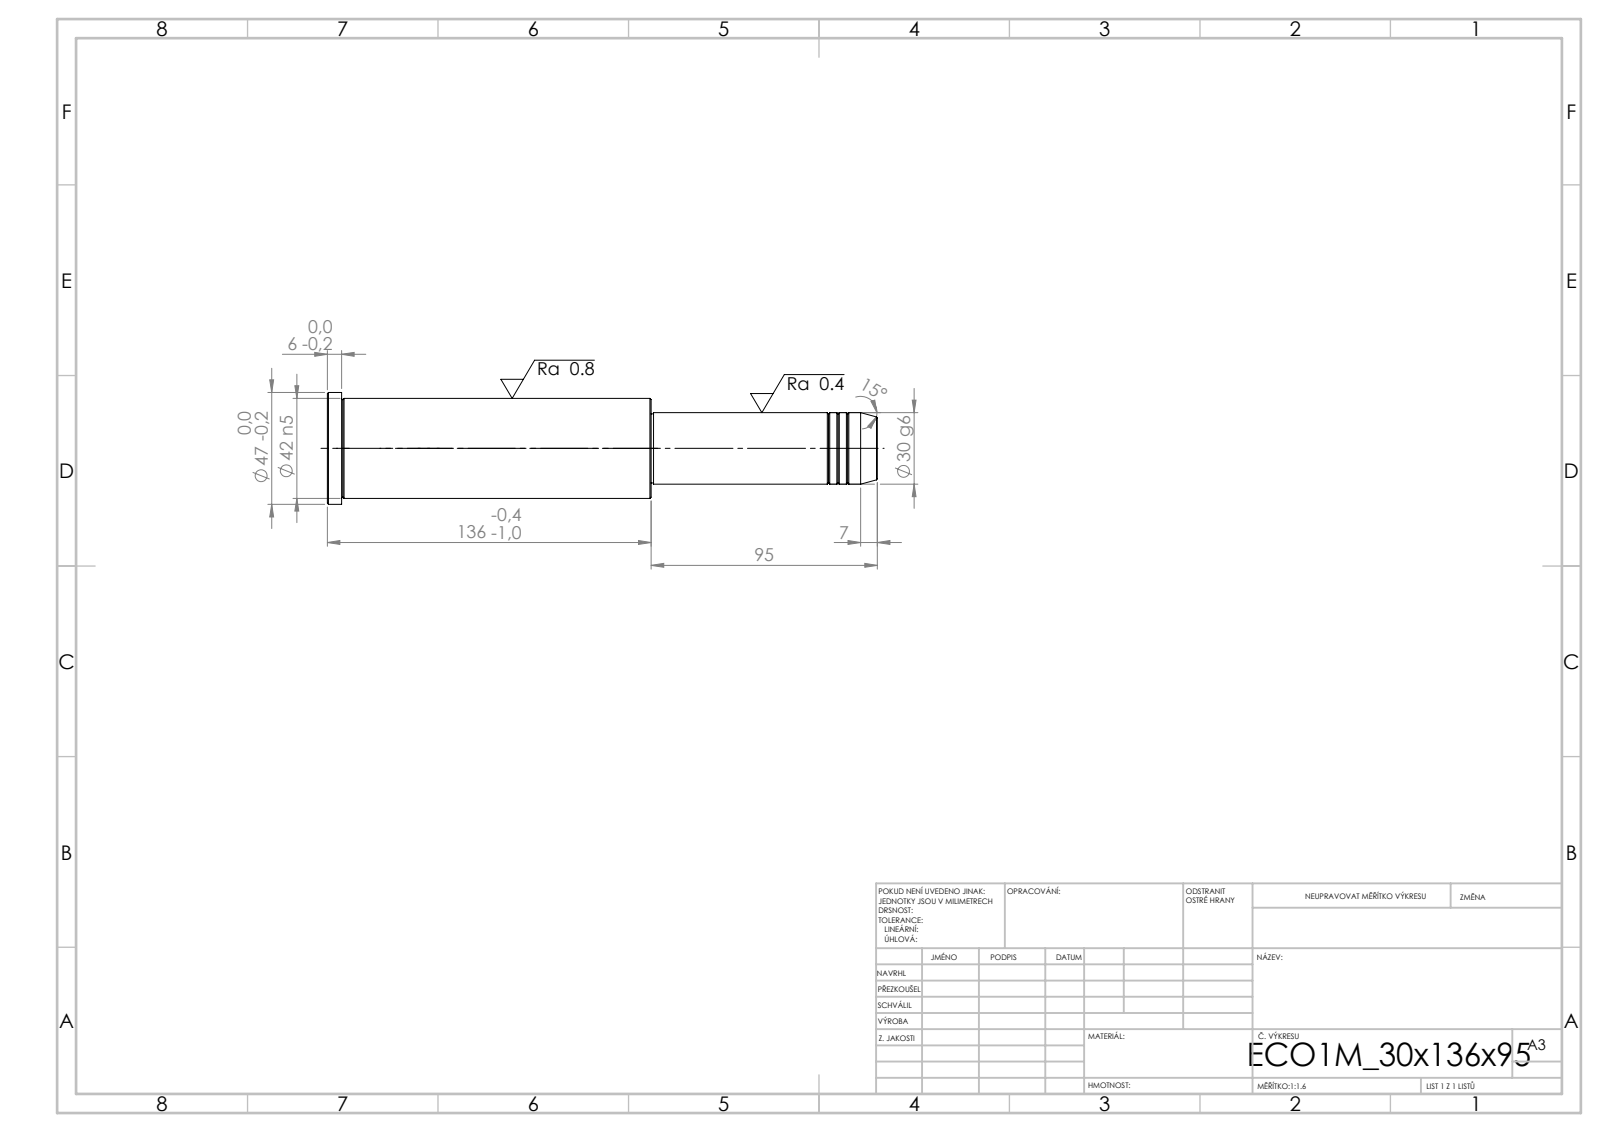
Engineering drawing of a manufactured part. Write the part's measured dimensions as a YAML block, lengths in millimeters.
step_written_by: "SolidWorks 2019 (CONFIG_CONTROL_DESIGN)"
units: millimeters
bodies: {solids: 1, faces: 43, planar: 5, cylindrical: 14, other: 24}
overall_size: [231, 47, 47]
volume: 256832
surface_area: 30499
round_bosses_or_shafts:
  - {diameter: 47, count: 1}
  - {diameter: 42, count: 1}
  - {diameter: 30, count: 1}
  - {diameter: 29, count: 1}
face_to_face_distances: [136, 95, 231, 225, 130, 6, 94, 1, 131, 137]
